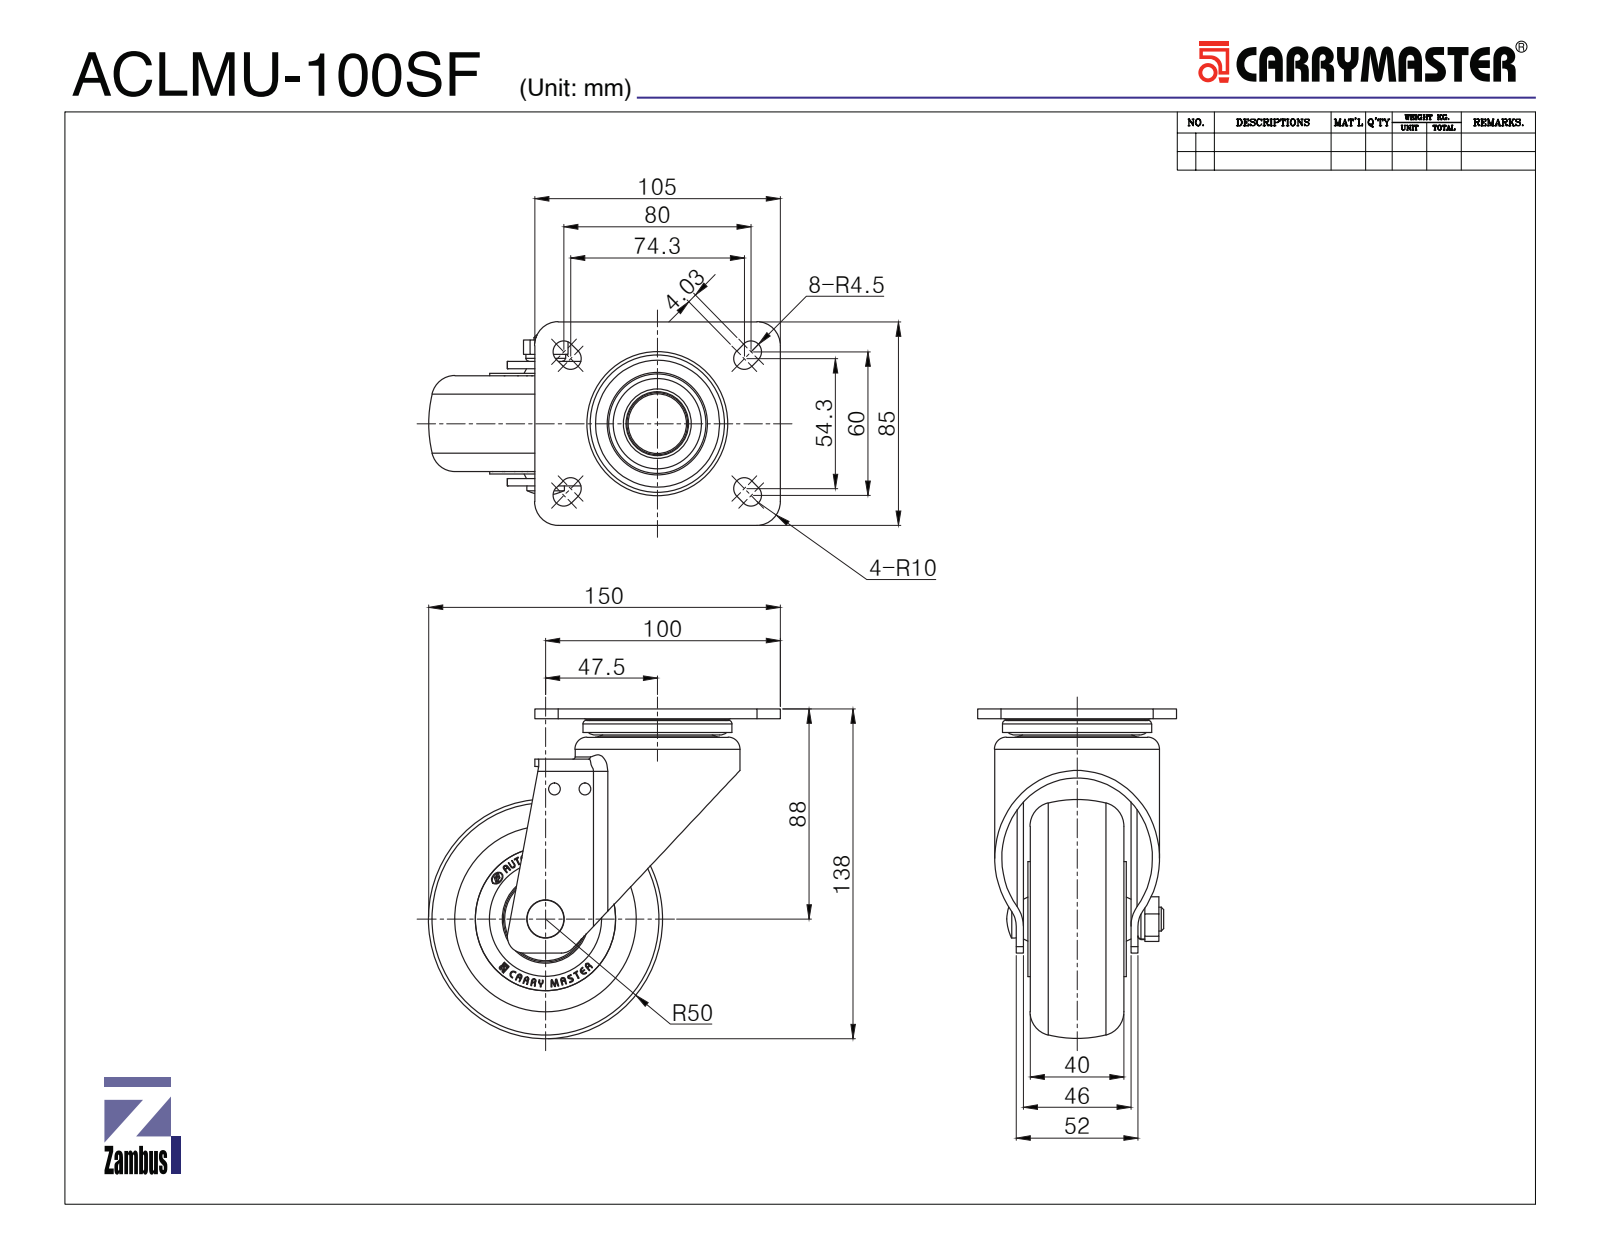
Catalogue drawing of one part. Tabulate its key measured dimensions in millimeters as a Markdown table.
| quantity | value |
| --- | --- |
| part name | ACLMU-100SF |
| STEP written by | SolidWorks 2015 (CONFIG_CONTROL_DESIGN) |
| units | millimeters |
| bodies | 13 solids, 1400 faces (763 planar, 197 cylindrical, 440 other) |
| overall size | 150.29 × 137.8 × 85 |
| volume | 417 843 mm³ |
| surface area | 137 211 mm² |
| round holes (diameter × count) | 1.7 × 2, 5 × 2, 8.5 × 1, 10 × 1, 12 × 1, 14.6 × 1, 30 × 1, 32 × 1, 32.08 × 1, 44.9 × 1, 51 × 1, 60 × 1 |
| round bosses / shafts (diameter × count) | 0.65 × 2, 80 × 1, 70.42 × 1, 63.7 × 1, 60.5 × 1, 57.3 × 1, 48 × 1, 35 × 1 |
| partial cylindrical surfaces (radius × count) | 1 × 32, 4.5 × 8, 1.5 × 4, 10 × 4, 0.64 × 2, 0.83 × 2, 1.17 × 2, 2 × 2 |
| main face-to-face distances | 3, 4, 46, 6, 2, 43, 49, 5, 1, 41 |
| hole center spacings | 27.92, 13, 37.97, 54.43, 56.85, 74.8, 76.29, 78.17 |
